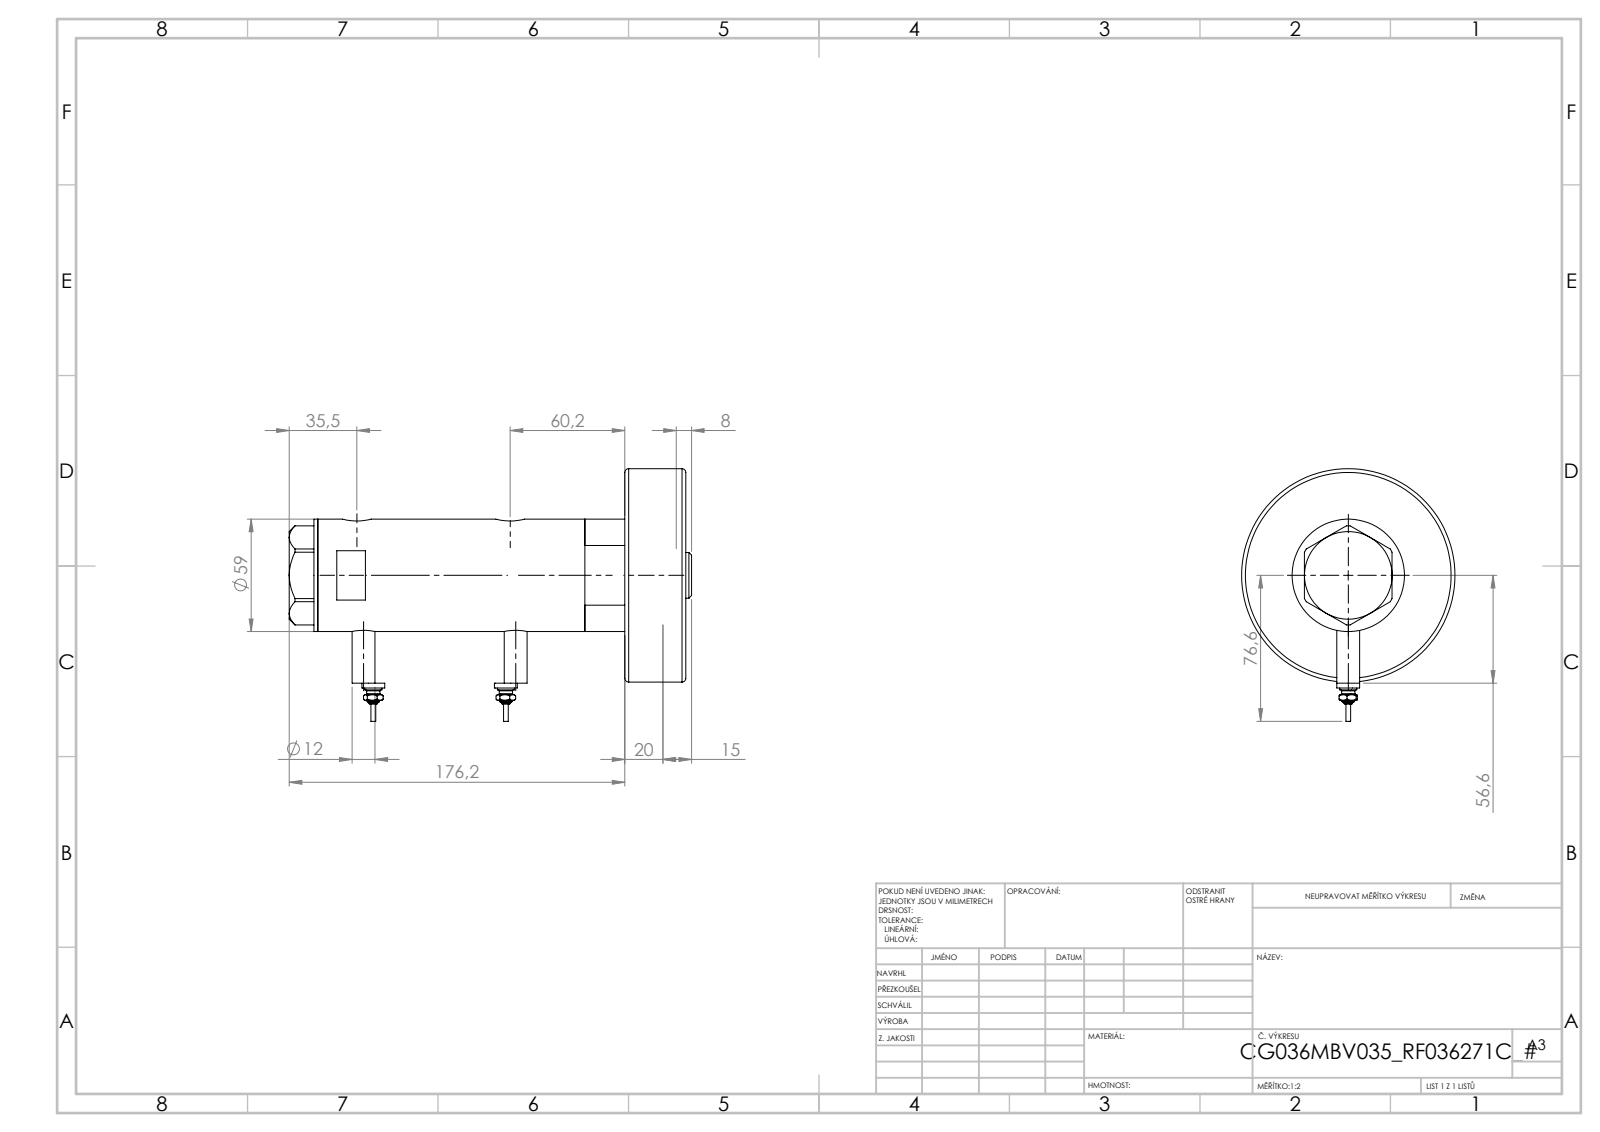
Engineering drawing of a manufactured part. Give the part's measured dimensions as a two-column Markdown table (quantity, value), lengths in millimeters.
| quantity | value |
| --- | --- |
| part name | V270CG_SWITCH; V270CG_VC; V270CG_BACK; V270CG_MIDDLE (+2 more) |
| STEP written by | SolidWorks 2019 (CONFIG_CONTROL_DESIGN) |
| units | millimeters |
| bodies | 7 solids, 242 faces (83 planar, 81 cylindrical, 78 other) |
| overall size | 198.42 × 117.8 × 112 |
| volume | 708 002 mm³ |
| surface area | 128 597 mm² |
| round holes (diameter × count) | 5 × 2, 9.73 × 2, 12.5 × 2, 15 × 2, 8.5 × 1, 25 × 1, 26.5 × 1, 36 × 1, 40 × 1, 48 × 1, 52 × 1 |
| round bosses / shafts (diameter × count) | 12 × 3, 9 × 2, 7 × 2, 4.34 × 2, 2.4 × 2, 112 × 1, 59 × 1, 46 × 1 |
| main face-to-face distances | 32, 145.84, 177.84, 92.34, 53.5, 85.5, 23.5, 68.84, 122.34, 154.34 |
| hole center spacings | 2.9, 3.5, 67.15, 70.05, 70.65, 73.55, 2.89, 2.91 |
